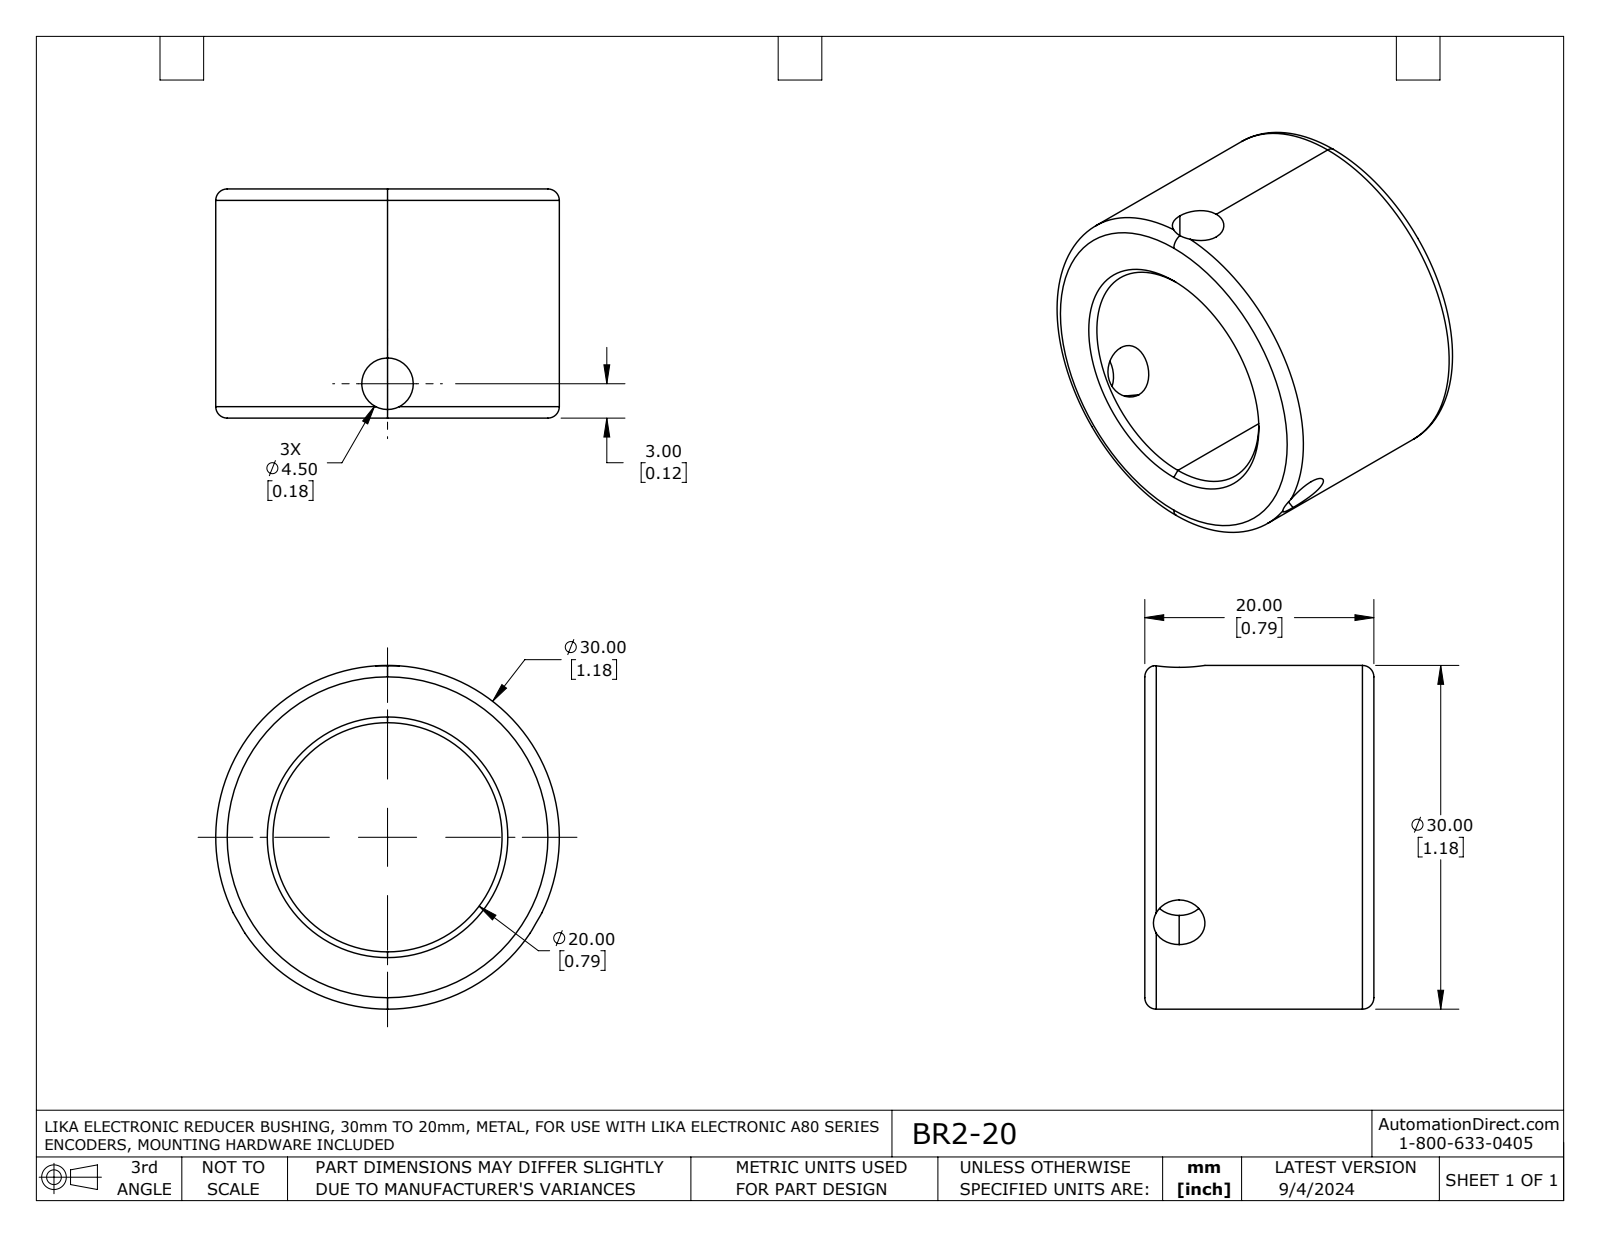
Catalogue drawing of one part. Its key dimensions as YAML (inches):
part_name: "BR2-20"
step_written_by: "SolidWorks 2021 (AUTOMOTIVE_DESIGN)"
units: inches
bodies: {solids: 1, faces: 25, planar: 2, cylindrical: 13, other: 10}
overall_size: [1.181, 1.181, 0.787]
volume: 0.461
surface_area: 6.086
round_holes:
  - {diameter: 0.177, count: 3}
  - {diameter: 0.787, count: 1}
round_bosses_or_shafts:
  - {diameter: 1.181, count: 1}
face_to_face_distances: [0.787]
